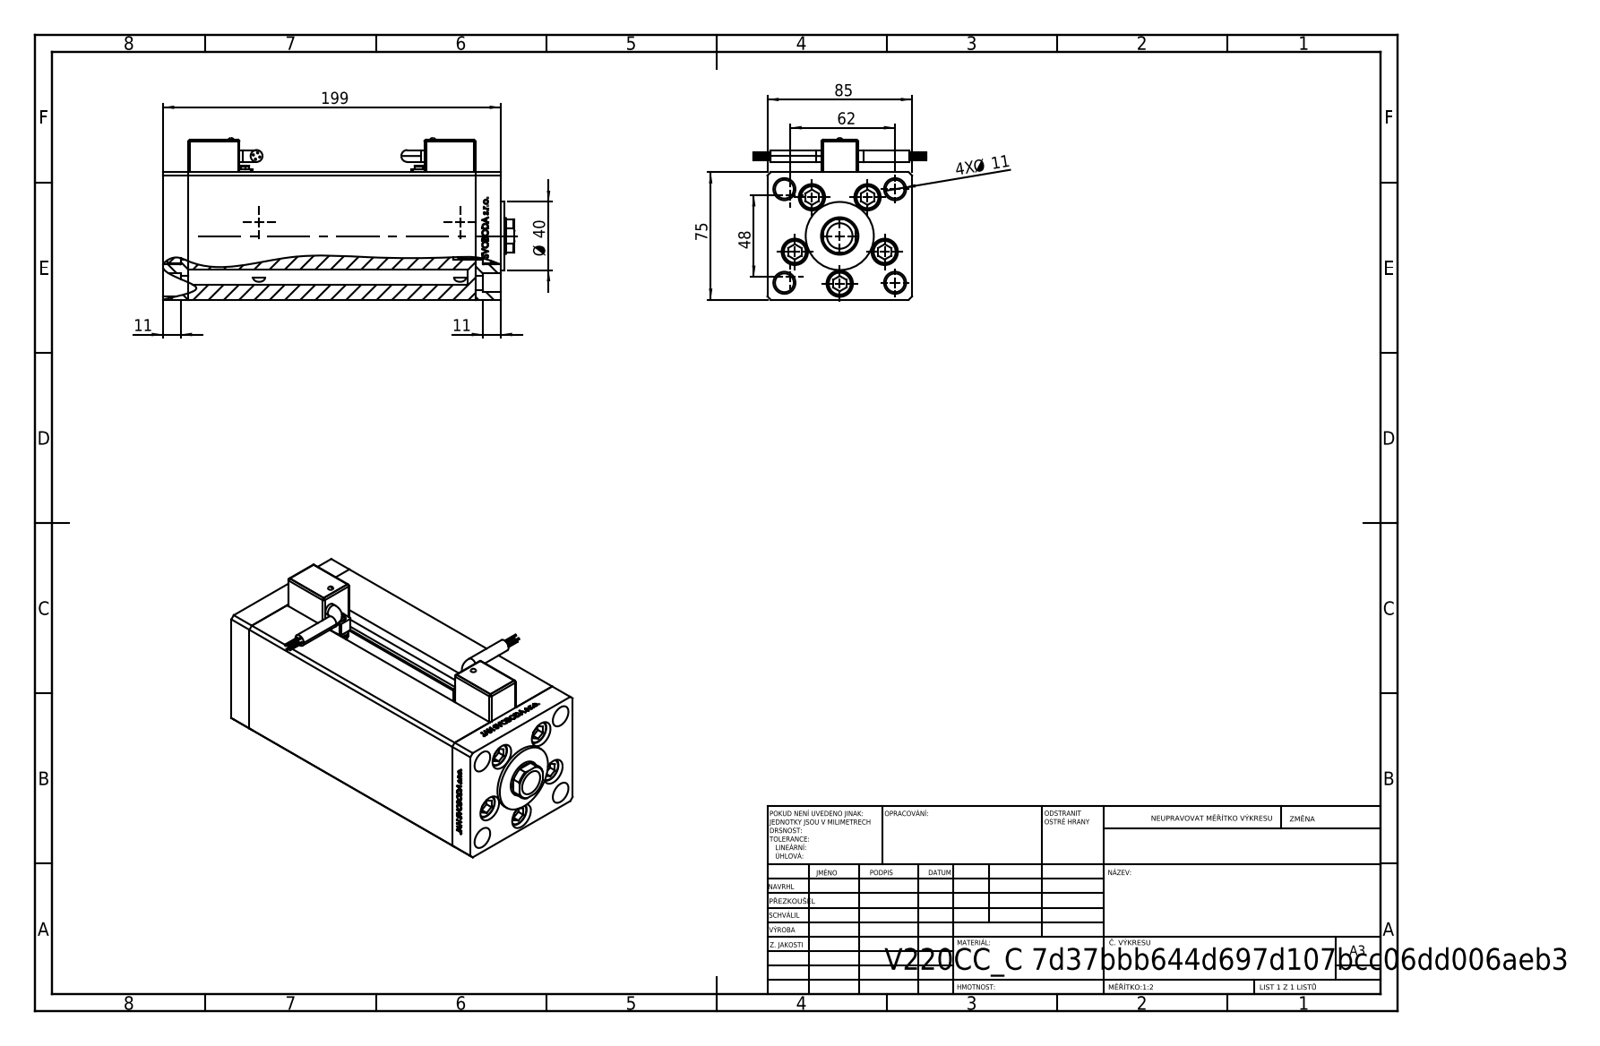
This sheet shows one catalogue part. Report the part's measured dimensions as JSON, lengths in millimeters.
{"part_name": "Magnetic_Switch_MSU4; V220C FRONT; V220C BACK; ALLEN BOLT (+2 more)", "step_written_by": "SolidWorks 2019 (CONFIG_CONTROL_DESIGN)", "units": "millimeters", "bodies": {"solids": 16, "faces": 1403, "planar": 634, "cylindrical": 265, "other": 504}, "overall_size": [206.5, 101.6, 95.1], "volume_mm3": 1100000, "surface_area_mm2": 201324, "round_holes": [[11, 9], [15.5, 5], [2, 4], [9, 4], [13, 4], [13.16, 4], [3.6, 2], [5, 2], [7, 2], [15, 1], [22, 1]], "round_bosses_or_shafts": [[0.85, 8], [14.5, 5], [8, 5], [7, 4], [6, 2], [3.5, 2], [2.5, 2], [40, 1]], "partial_cylinders_radius": [[1, 24], [4, 4], [0.93, 2], [10.5, 1]], "face_to_face_distances": [85, 75, 168.5, 15, 183.5, 10.5, 68.5, 198.5, 6.5, 4.5], "hole_center_spacings": [28, 4.95, 37.64, 42.57, 51.62, 61.6, 80.22, 8.25]}
